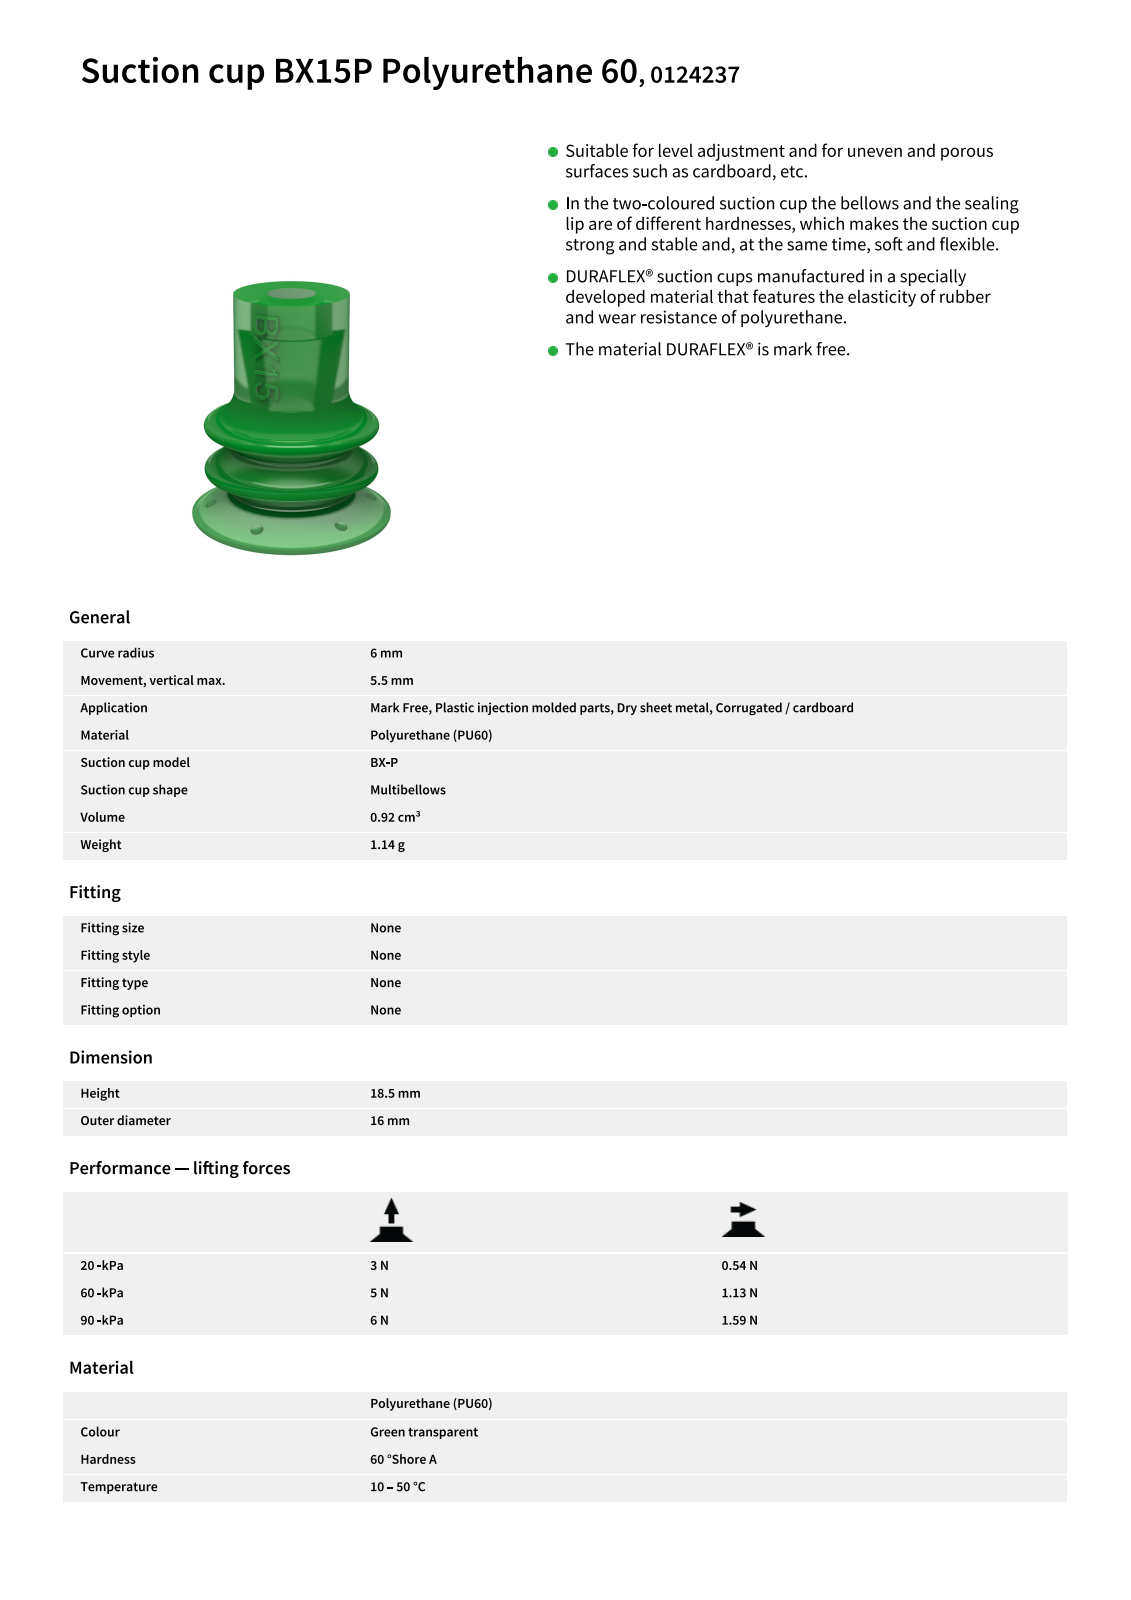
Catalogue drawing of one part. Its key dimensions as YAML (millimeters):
part_name: "0118505-1; 0118505-2"
step_written_by: "Unknown (automotive_design)"
units: millimeters
bodies: {solids: 4, faces: 162, planar: 56, cylindrical: 22, other: 84}
overall_size: [18.45, 16, 16]
volume: 1844
surface_area: 3354
round_holes:
  - {diameter: 3.8, count: 1}
round_bosses_or_shafts:
  - {diameter: 16, count: 1}
  - {diameter: 9, count: 1}
partial_cylinders:
  - {radius: 4.7, count: 1}
face_to_face_distances: [16.45, 2, 18.45, 15.45, 13.45, 3, 13.11, 11.11, 2.34, 5.34]
